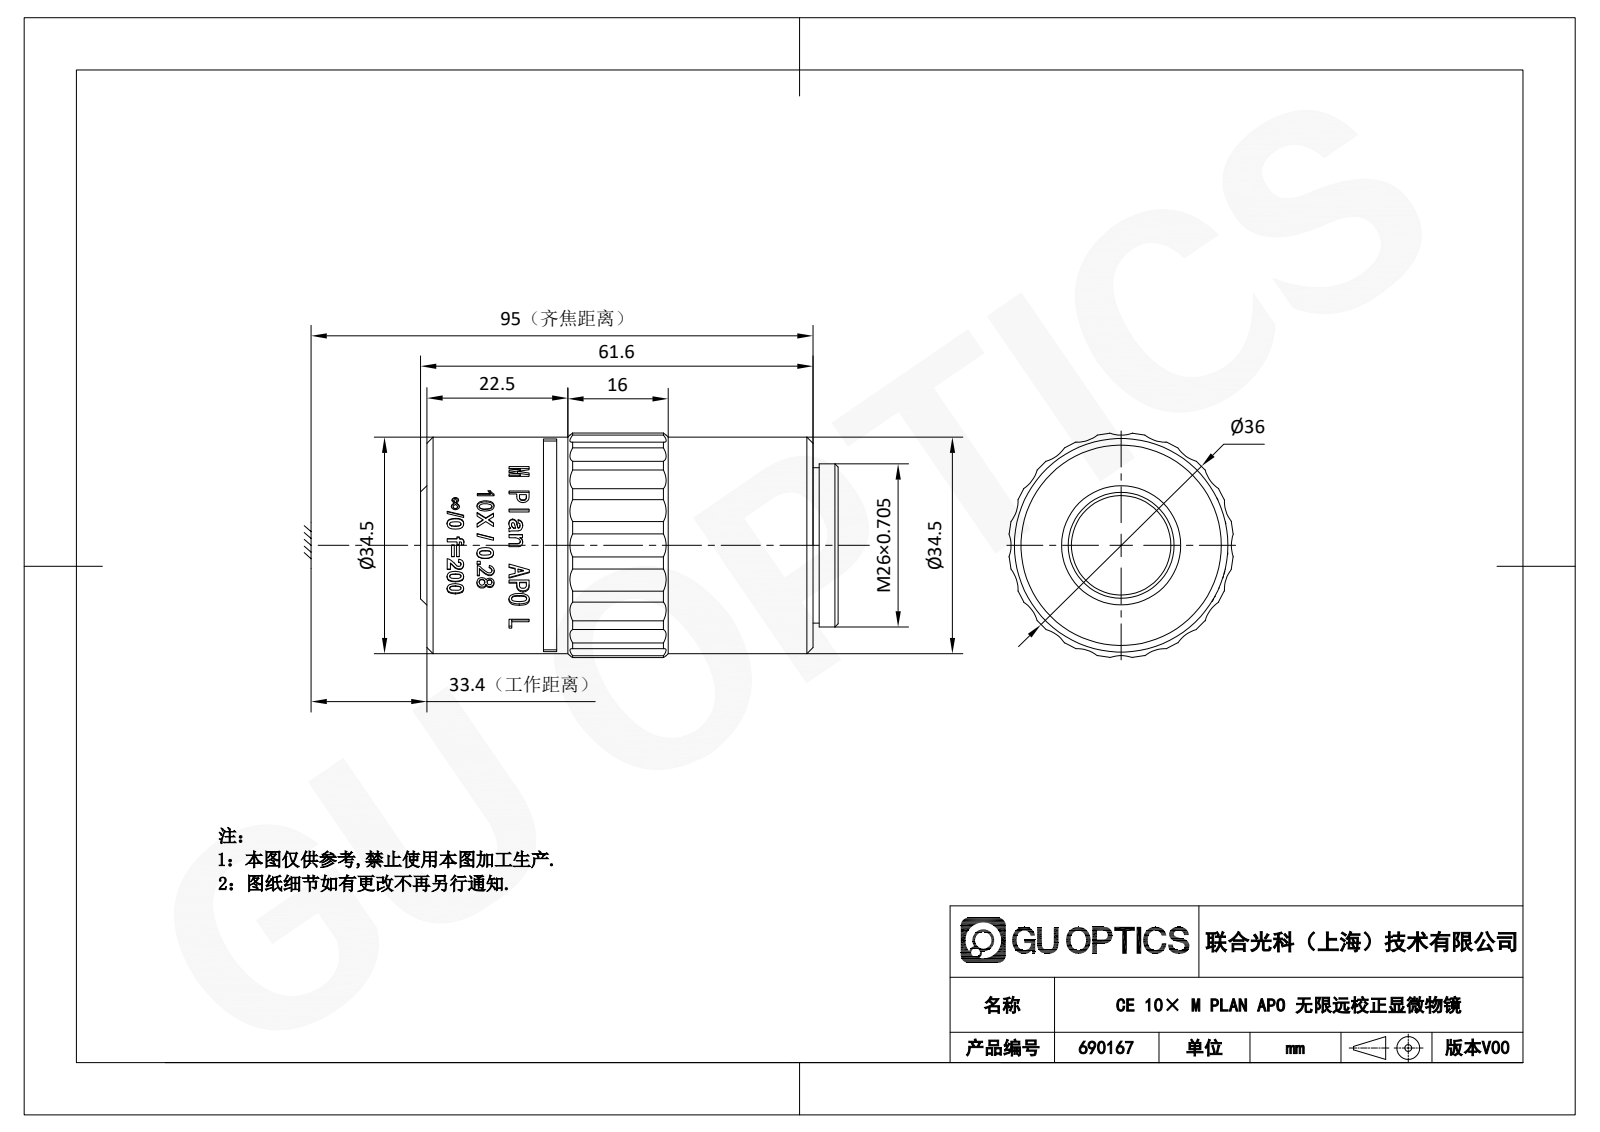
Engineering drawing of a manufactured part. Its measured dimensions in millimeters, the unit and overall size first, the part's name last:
Units: millimetres
Overall size (bounding box): 65.61 × 35.81 × 35.81
Round holes (diameter × count): ⌀15 ×1, ⌀22 ×1
Round bosses / shafts (diameter × count): ⌀34.5 ×1, ⌀33.88 ×1, ⌀26 ×1, ⌀24.8 ×1
Partial cylindrical surfaces — rounded edges, fillets, slot ends (radius × count): R5.29 ×20, R16.84 ×1, R17.05 ×1, R18 ×1
Main face-to-face distances: 61.91, 1.31, 60.6, 0.5, 62.41, 61.1, 2.7, 4.01, 64.61, 65.11
Volume: 58 638 mm³ · Surface area: 9 234 mm²
Bodies: 1 solid, 377 faces (110 planar, 97 cylindrical, 170 other)
Part name (STEP PRODUCT): 690165
STEP written by: SolidWorks 2020 (CONFIG_CONTROL_DESIGN)
